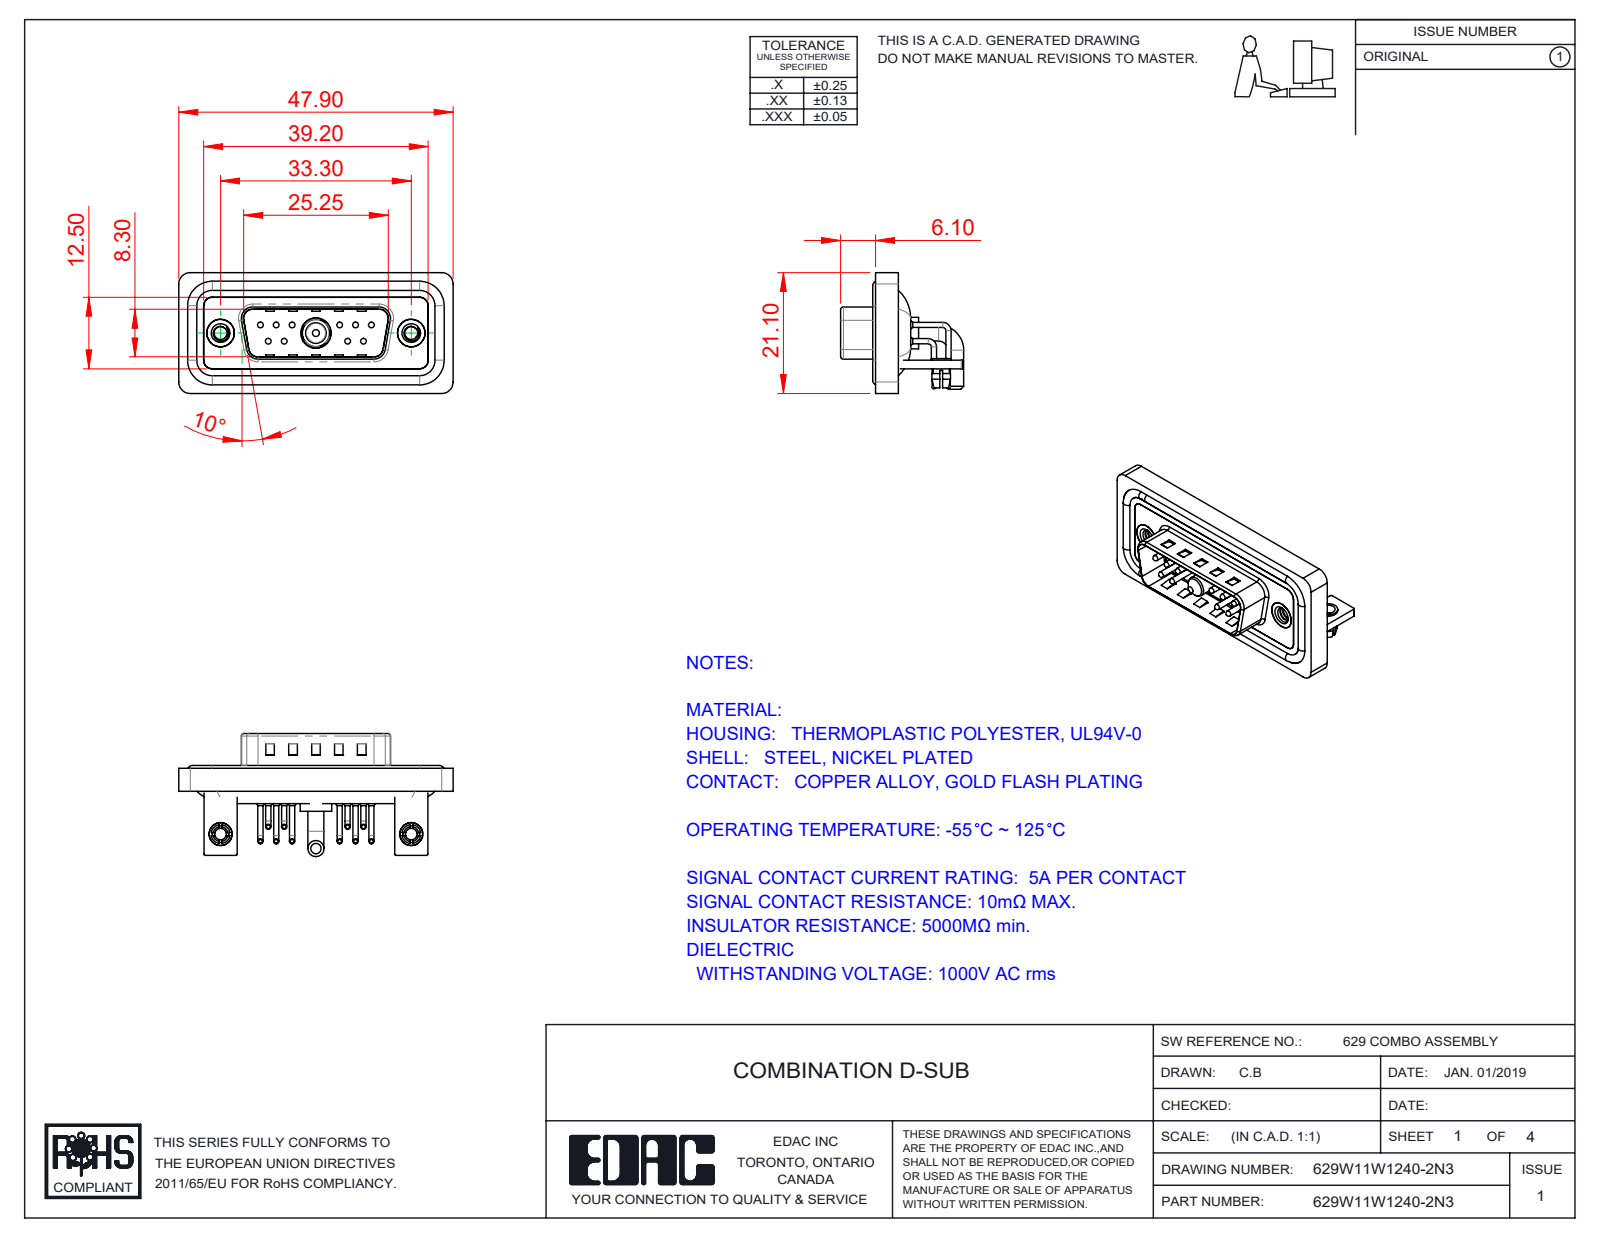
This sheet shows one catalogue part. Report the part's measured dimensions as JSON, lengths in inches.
{"part_name": "629Combo Stabilizer Bracket; 629Combo Board Lock; 629Combo Contact Row 1; Power Pin_20A RA (+7 more)", "step_written_by": "SolidWorks 2020 (CONFIG_CONTROL_DESIGN)", "units": "inches", "bodies": {"solids": 23, "faces": 1735, "planar": 904, "cylindrical": 619, "other": 212}, "overall_size": [1.886, 0.846, 0.831], "volume_in3": 0.36, "surface_area_in2": 15.62, "round_holes": [[0.079, 12], [0.03, 10], [0.063, 10], [0.089, 2], [0.098, 2], [0.126, 2], [0.157, 2], [0.189, 2], [0.197, 2], [0.191, 1], [0.209, 1]], "round_bosses_or_shafts": [[0.035, 20], [0.059, 10], [0.039, 10], [0.026, 10], [0.063, 4], [0.193, 2], [0.157, 2], [0.134, 2]], "partial_cylinders_radius": [[0.079, 21], [0.059, 18], [0.01, 16], [0.04, 10], [0.02, 9], [0.063, 8], [0.039, 7], [0.024, 4]], "face_to_face_distances": [0.016, 0.031, 0.059, 0.114, 0.083, 0.043, 0.063, 0.047, 0.146, 0.161], "hole_center_spacings": [0.124, 0.109, 0.545, 0.436, 0.654, 0.198, 0.198, 0.218]}
